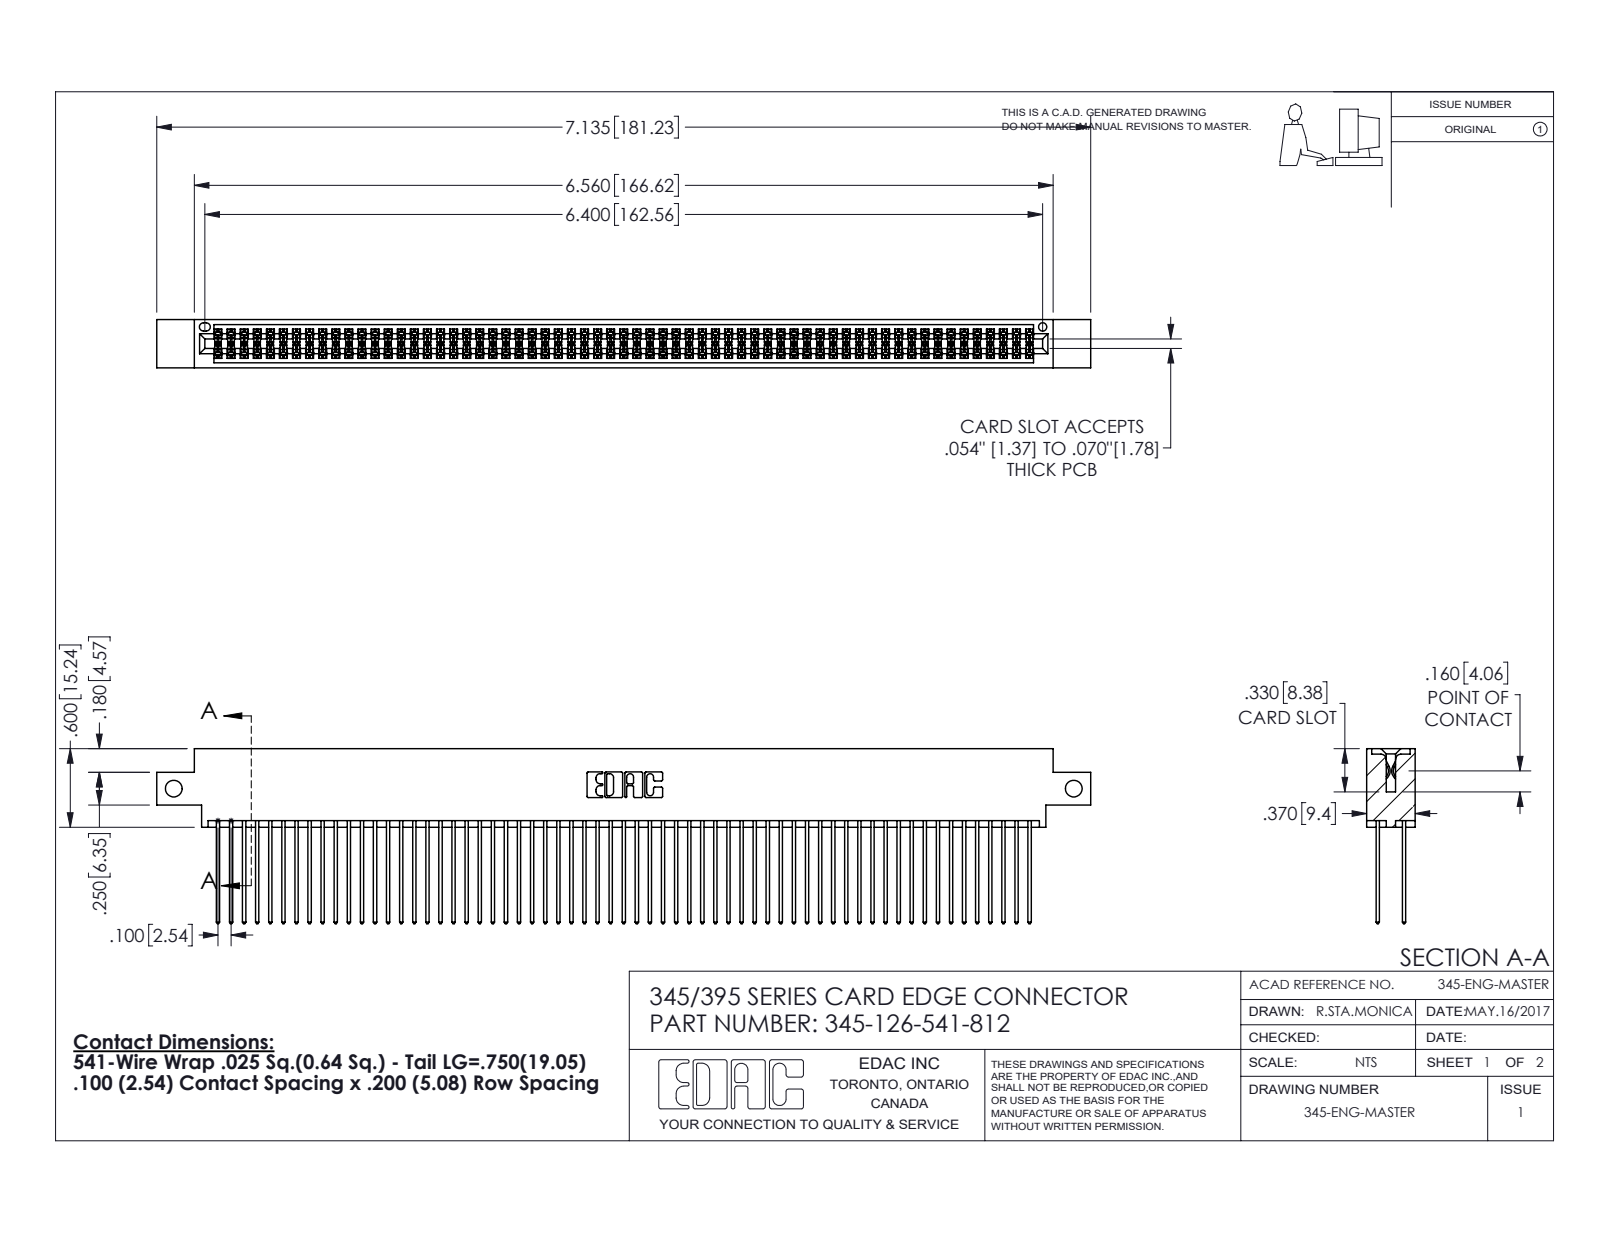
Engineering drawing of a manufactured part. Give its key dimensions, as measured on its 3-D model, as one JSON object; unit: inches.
{"part_name": "345-126-541-812; 345 Part_0.170 Offset - Side Mount; 345-292-001_345-293-141", "step_written_by": "SolidWorks 2016 (CONFIG_CONTROL_DESIGN)", "units": "inches", "bodies": {"solids": 127, "faces": 6430, "planar": 4242, "cylindrical": 2188, "other": 0}, "overall_size": [7.135, 1.337, 0.37], "volume_in3": 1.118, "surface_area_in2": 47.89, "round_holes": [[0.128, 2], [0.064, 1]], "partial_cylinders_radius": [[0.006, 189], [0.01, 126], [0.01, 22], [0.007, 6], [0.031, 6], [0.026, 3], [0.014, 2], [0.019, 2]], "face_to_face_distances": [0.298, 0.072, 0.2, 0.098, 0.272, 0.025, 0.225, 0.37, 0.175, 0.149], "hole_center_spacings": [6.875]}
